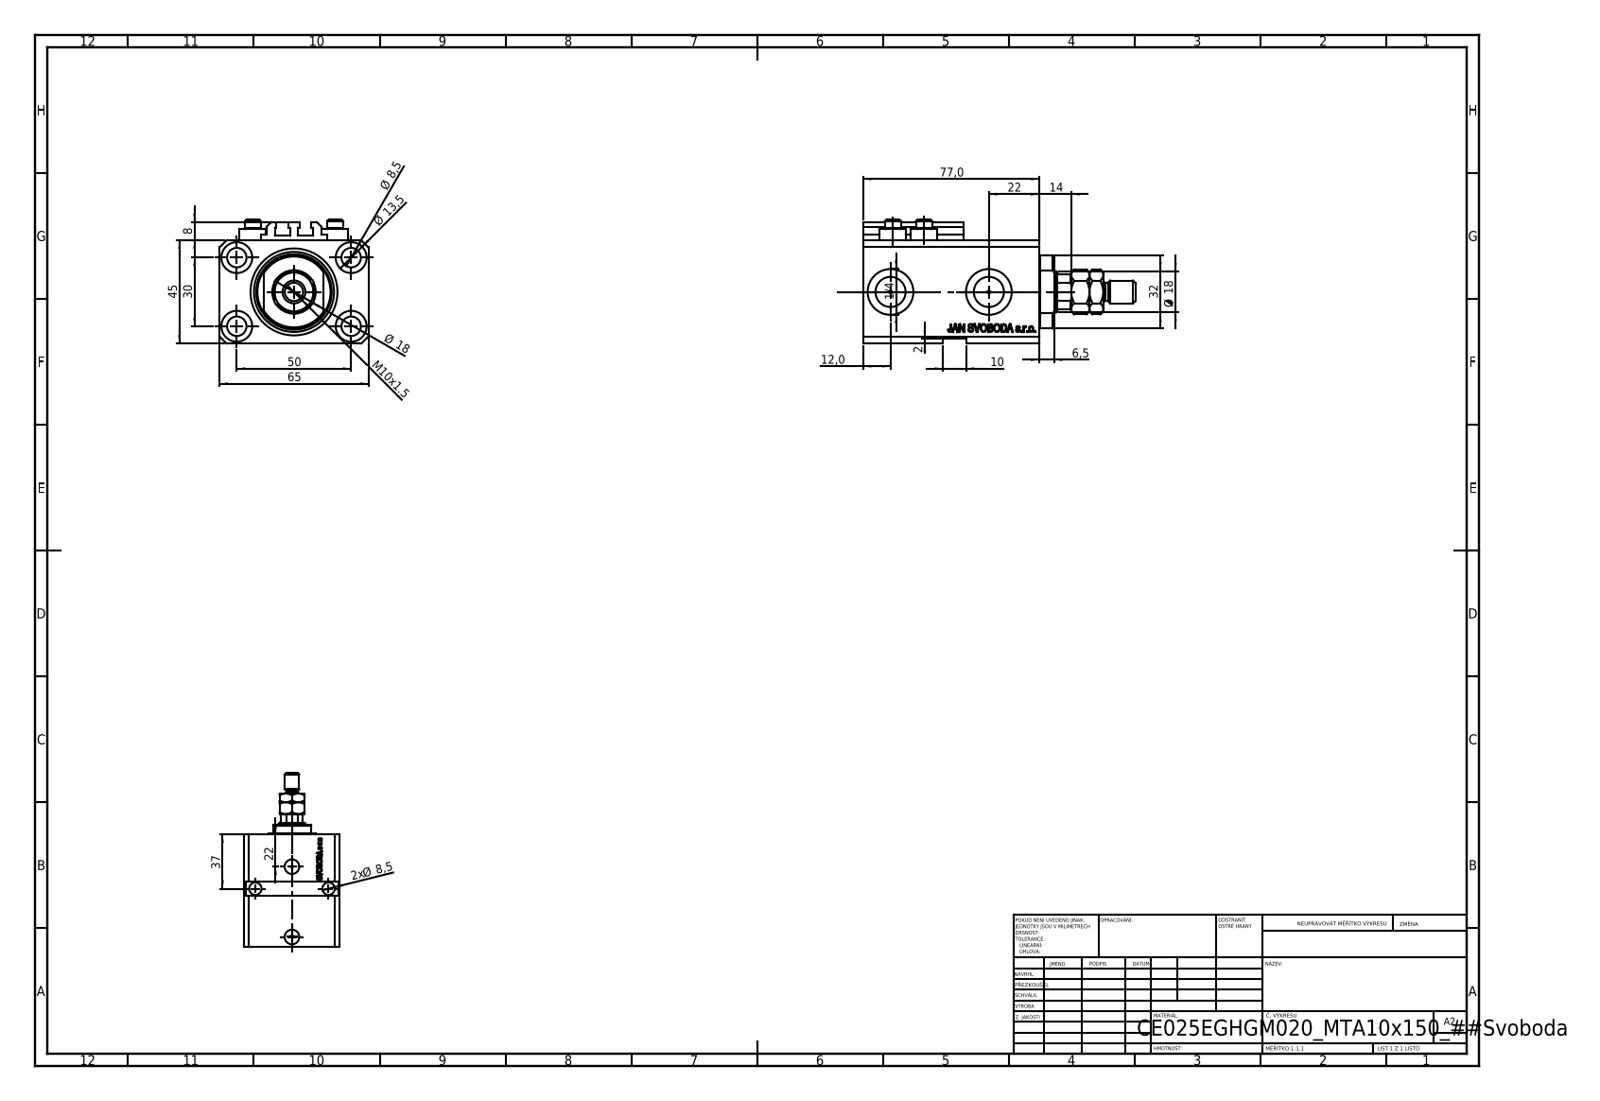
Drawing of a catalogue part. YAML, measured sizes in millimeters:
part_name: "V250CE_C_VCP; V250CE_VC_E; MTA; ALLEN BOLT V250CE (+1 more)"
step_written_by: "SolidWorks 2019 (CONFIG_CONTROL_DESIGN)"
units: millimeters
bodies: {solids: 9, faces: 1116, planar: 526, cylindrical: 130, other: 460}
overall_size: [119, 65, 54]
volume: 204261
surface_area: 60923
round_holes:
  - {diameter: 8.5, count: 7}
  - {diameter: 1.25, count: 4}
  - {diameter: 4, count: 4}
  - {diameter: 13.5, count: 4}
  - {diameter: 10, count: 2}
  - {diameter: 13.16, count: 2}
  - {diameter: 20, count: 2}
  - {diameter: 18, count: 1}
  - {diameter: 25, count: 1}
  - {diameter: 38, count: 1}
round_bosses_or_shafts:
  - {diameter: 11.6, count: 4}
  - {diameter: 7, count: 4}
  - {diameter: 10, count: 1}
  - {diameter: 8, count: 1}
partial_cylinders:
  - {radius: 0.2, count: 10}
  - {radius: 8.5, count: 1}
  - {radius: 16, count: 1}
face_to_face_distances: [45, 65, 14, 63, 77, 2, 6.9, 56.1, 70.1, 20.5]
hole_center_spacings: [29.15, 50, 13.6, 15.12, 18.81, 18.97, 26.22, 26.61]
